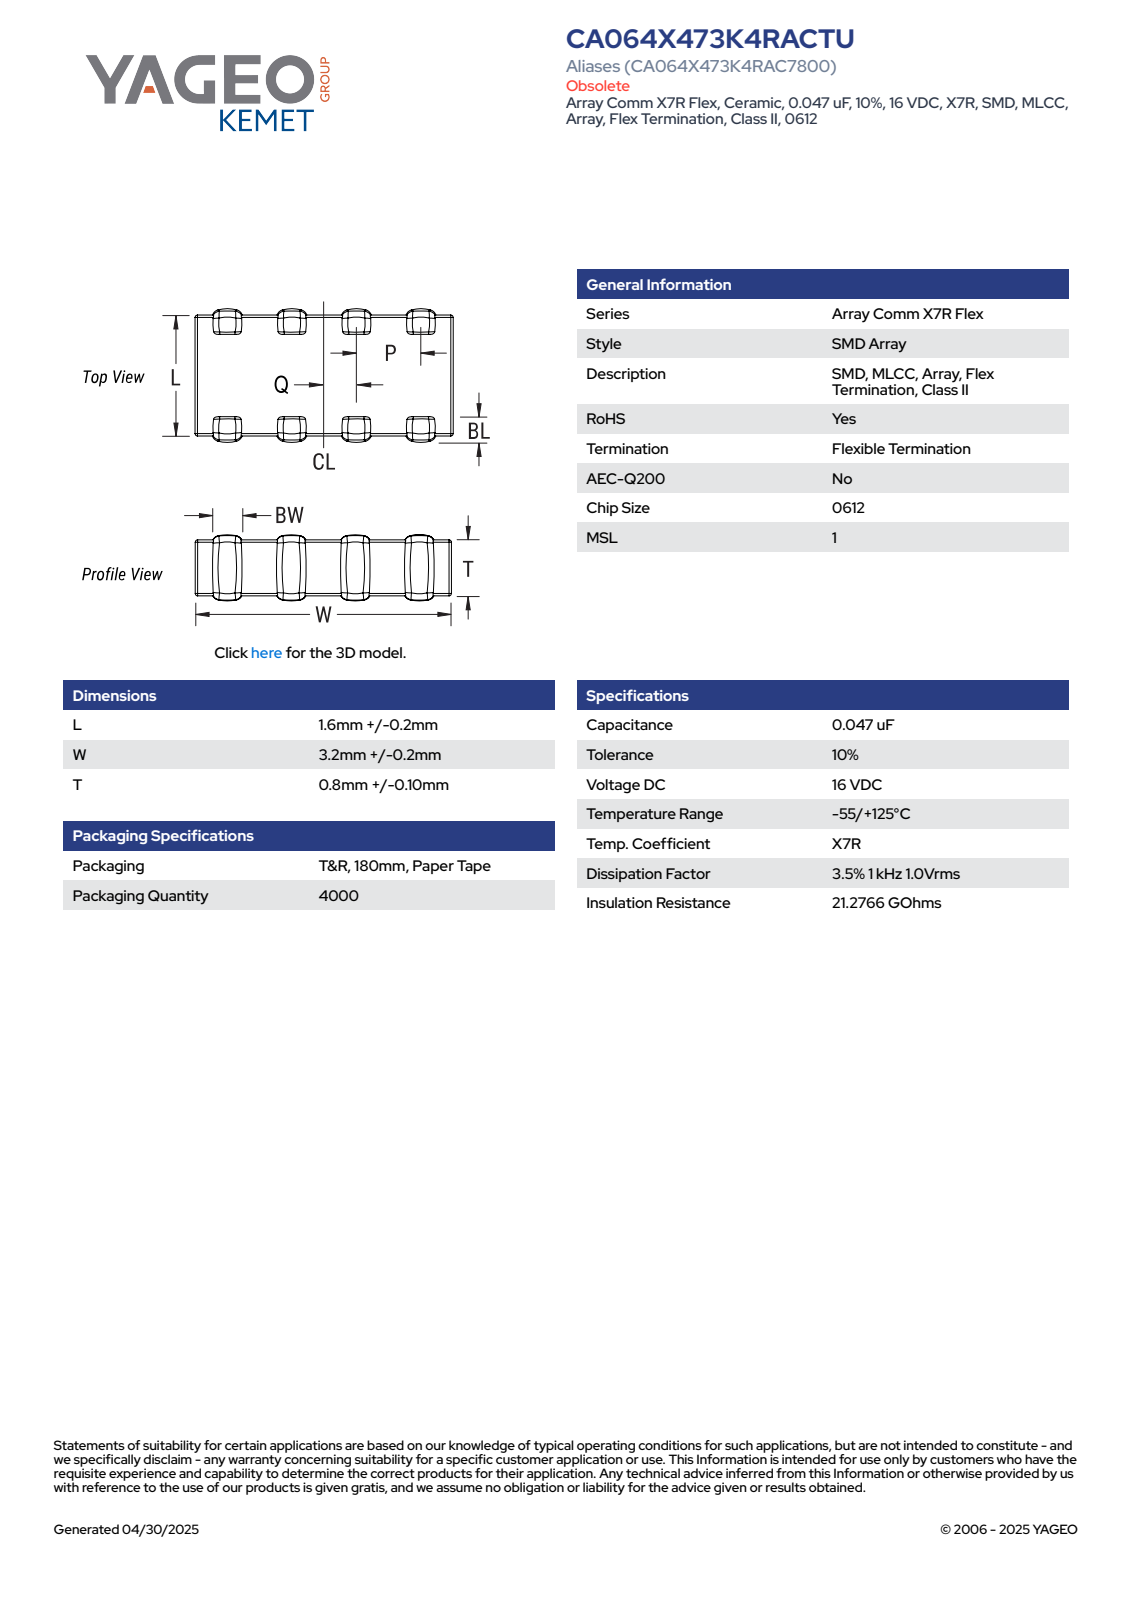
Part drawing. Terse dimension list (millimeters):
name: CCN_A4K_0612_L1.8W3.4T0.9P0.8
written by: SolidWorks 2021 (AUTOMOTIVE_DESIGN)
unit: mm
bodies: 4 solids, 323 faces (127 planar, 132 cylindrical, 64 other)
size: 3.4 × 1.9 × 1
volume: 6 mm³; area: 24 mm²
rounds: 16× R0.1
face distances: 0.9, 1.85, 0.95, 1.8, 3.4, 1.9, 1, 0.4, 1.7, 0.8
